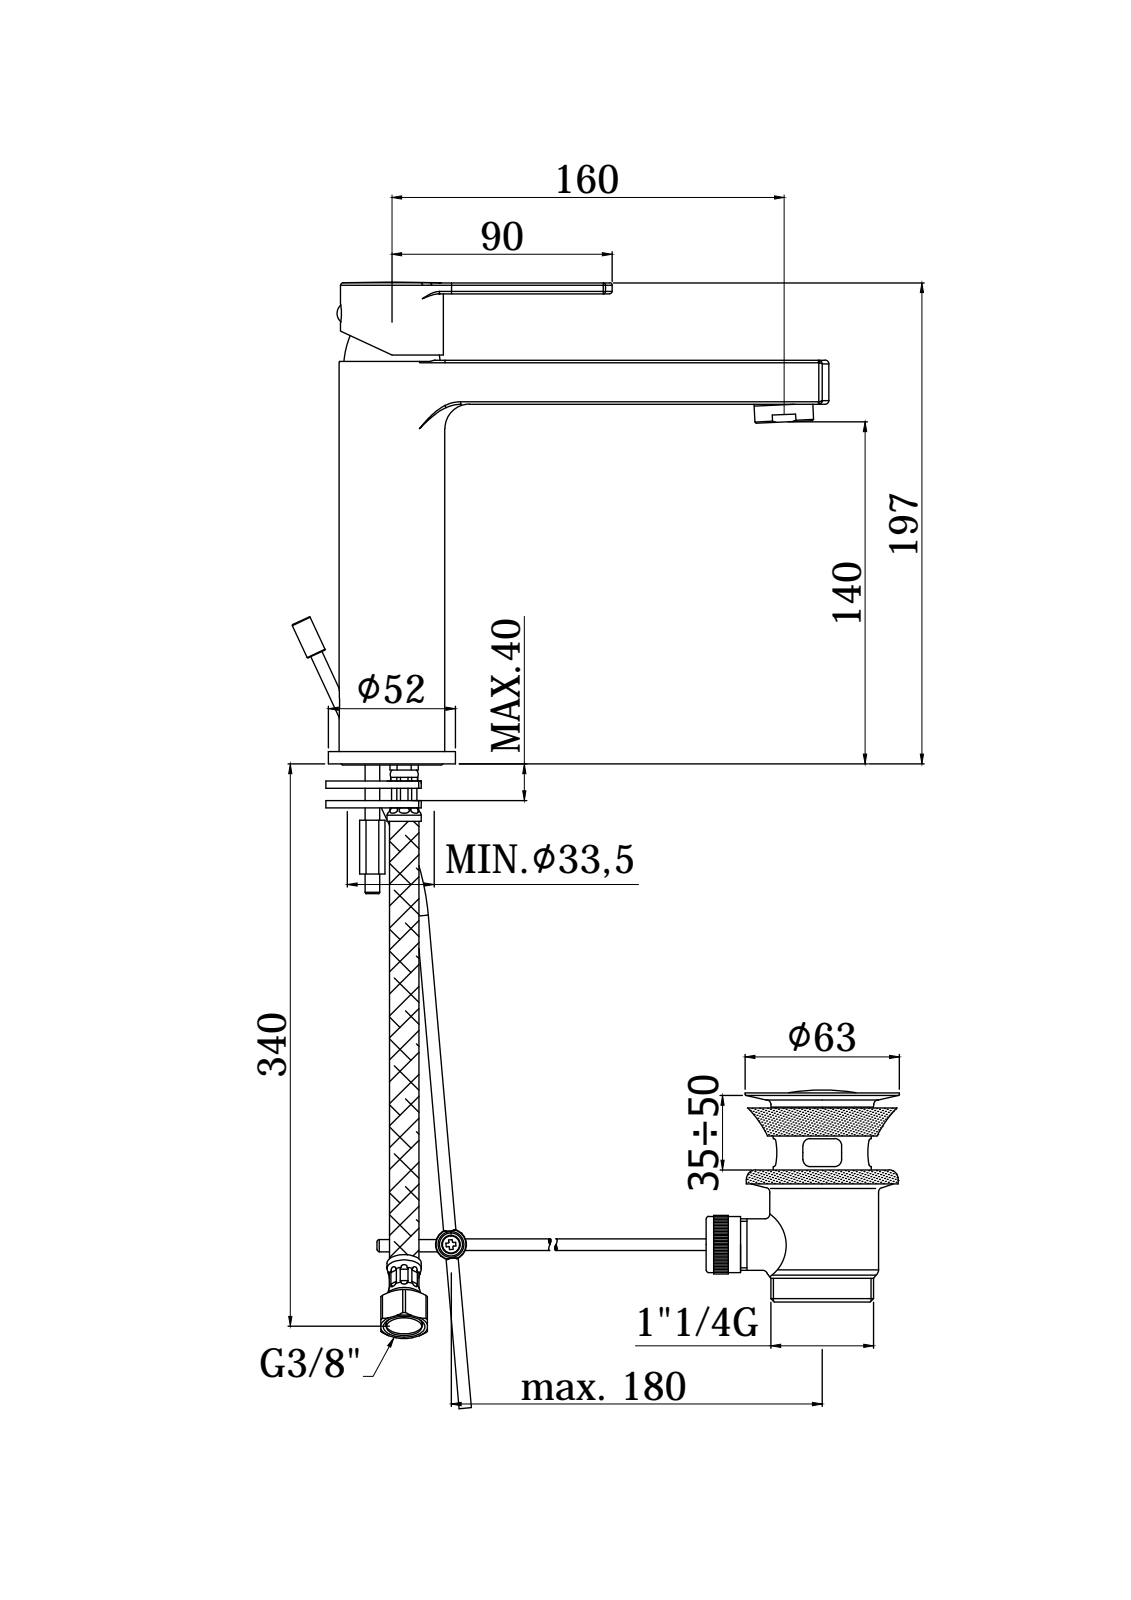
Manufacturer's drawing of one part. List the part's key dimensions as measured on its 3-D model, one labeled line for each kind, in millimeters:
Part name (STEP PRODUCT): RIN073CR
STEP written by: CREO PARAMETRIC BY PTC INC, 2020044 (CONFIG_CONTROL_DESIGN)
Units: millimetres
Bodies: 5 solids, 3405 faces (2420 planar, 545 cylindrical, 440 other)
Overall size (bounding box): 219.35 × 196.42 × 52
Volume: 185 640 mm³ · Surface area: 125 608 mm²
Round holes (diameter × count): ⌀6 ×4, ⌀8.2 ×4, ⌀4 ×3, ⌀5 ×3, ⌀5.5 ×2, ⌀6.5 ×2, ⌀7 ×2, ⌀8 ×2, ⌀9 ×2, ⌀3 ×1, ⌀3.3 ×1, ⌀3.4 ×1
Round bosses / shafts (diameter × count): ⌀8 ×7, ⌀4 ×3, ⌀11 ×2, ⌀9 ×2, ⌀6.8 ×2, ⌀6 ×2, ⌀4.8 ×2, ⌀52 ×1
Partial cylindrical surfaces — rounded edges, fillets, slot ends (radius × count): R0.5 ×44, R1 ×28, R1.5 ×14, R2 ×9, R1.7 ×6, R0.8 ×4, R5.8 ×4, R20 ×4
Main face-to-face distances: 3.5, 14.5, 18, 11, 27.5, 1, 31, 2.5, 24, 30.05
Hole centre spacings: 14, 13.6, 2.83, 8.6, 9.26, 11.77, 13.45, 15.13
